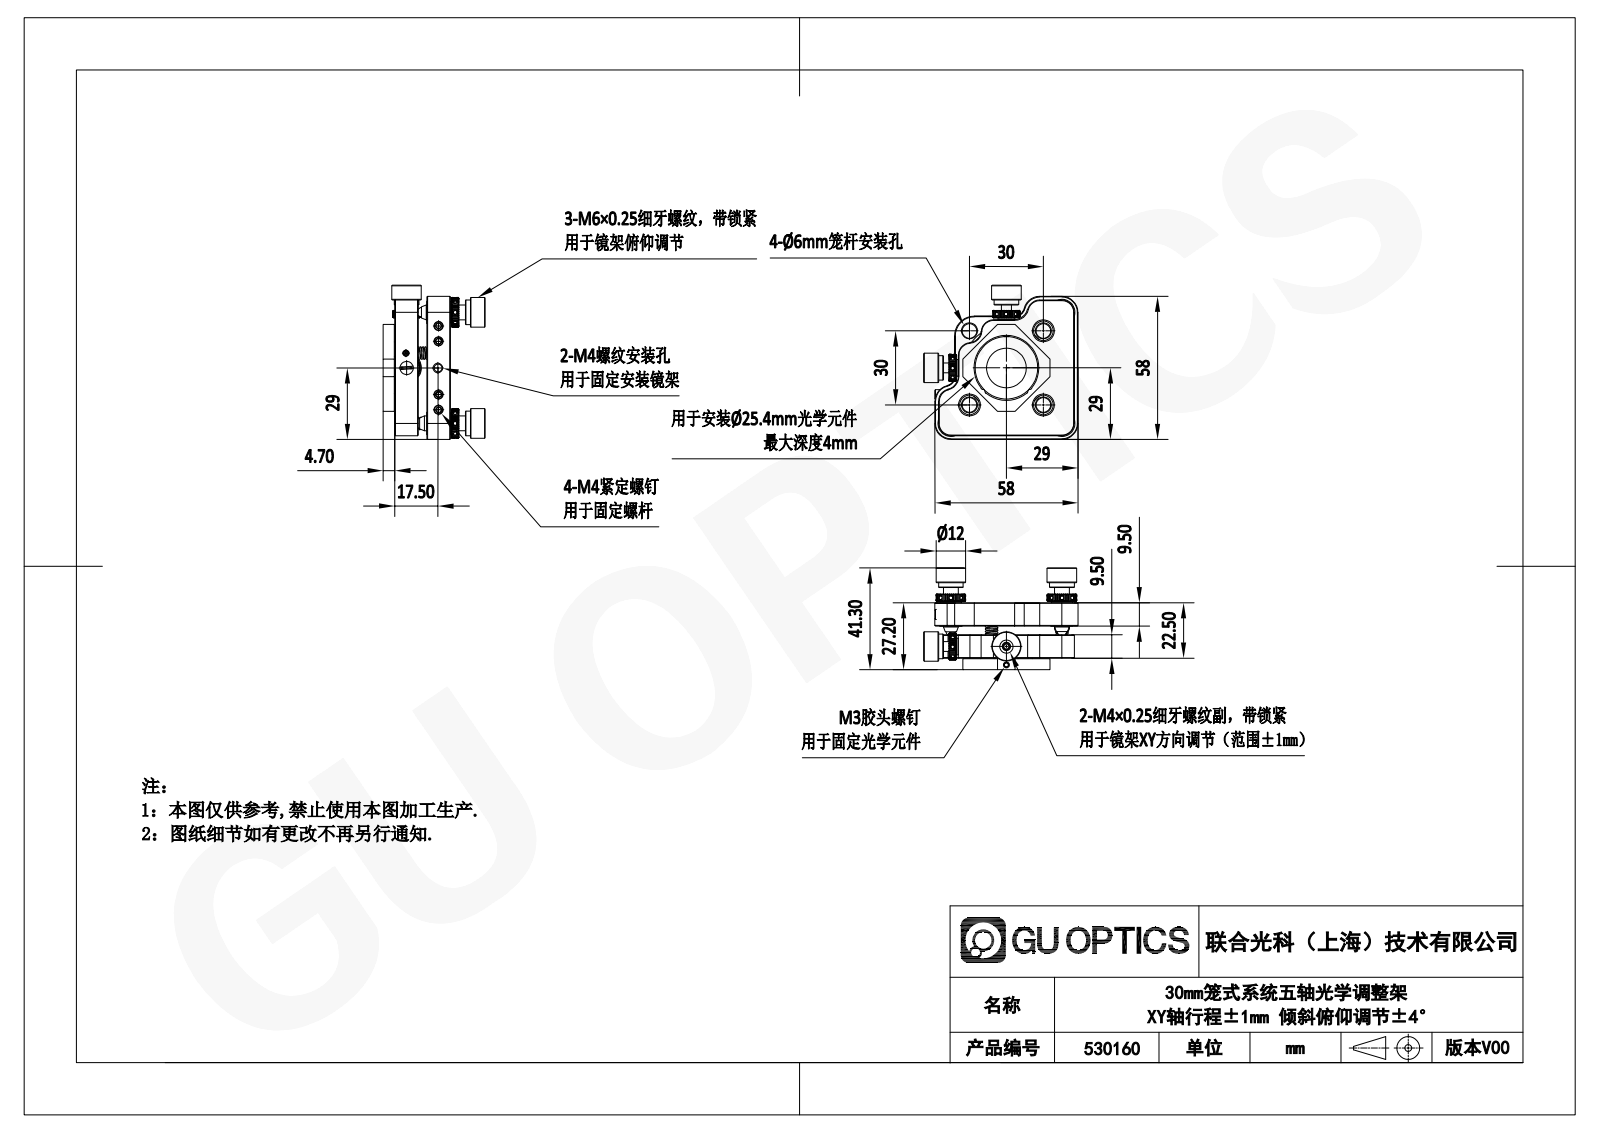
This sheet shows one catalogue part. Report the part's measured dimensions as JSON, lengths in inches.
{"part_name": "530160", "step_written_by": "SolidWorks 2020 (CONFIG_CONTROL_DESIGN)", "units": "inches", "bodies": {"solids": 48, "faces": 2831, "planar": 1191, "cylindrical": 575, "other": 1065}, "overall_size": [2.461, 2.461, 1.626], "volume_in3": 2.505, "surface_area_in2": 49.74, "round_holes": [[0.059, 23], [0.236, 9], [0.13, 6], [0.098, 5], [0.157, 5], [0.217, 5], [0.039, 4], [0.157, 3], [0.315, 3], [0.122, 2], [0.138, 2], [0.148, 2]], "round_bosses_or_shafts": [[0.472, 5], [0.394, 5], [0.157, 4], [0.374, 3], [0.339, 3], [0.299, 3], [0.197, 3], [0.079, 3]], "partial_cylinders_radius": [[0.098, 8], [0.039, 6], [0.256, 5], [0.031, 4], [0.04, 4], [0.197, 4], [0.217, 4], [0.169, 3]], "face_to_face_distances": [0.374, 0.512, 0.138, 0.886, 0.059, 0.52, 0.315, 0.402, 0.177, 0.028], "hole_center_spacings": [1.253, 1.506, 0.102, 0.835, 0.927, 1.178, 1.181, 1.772]}
